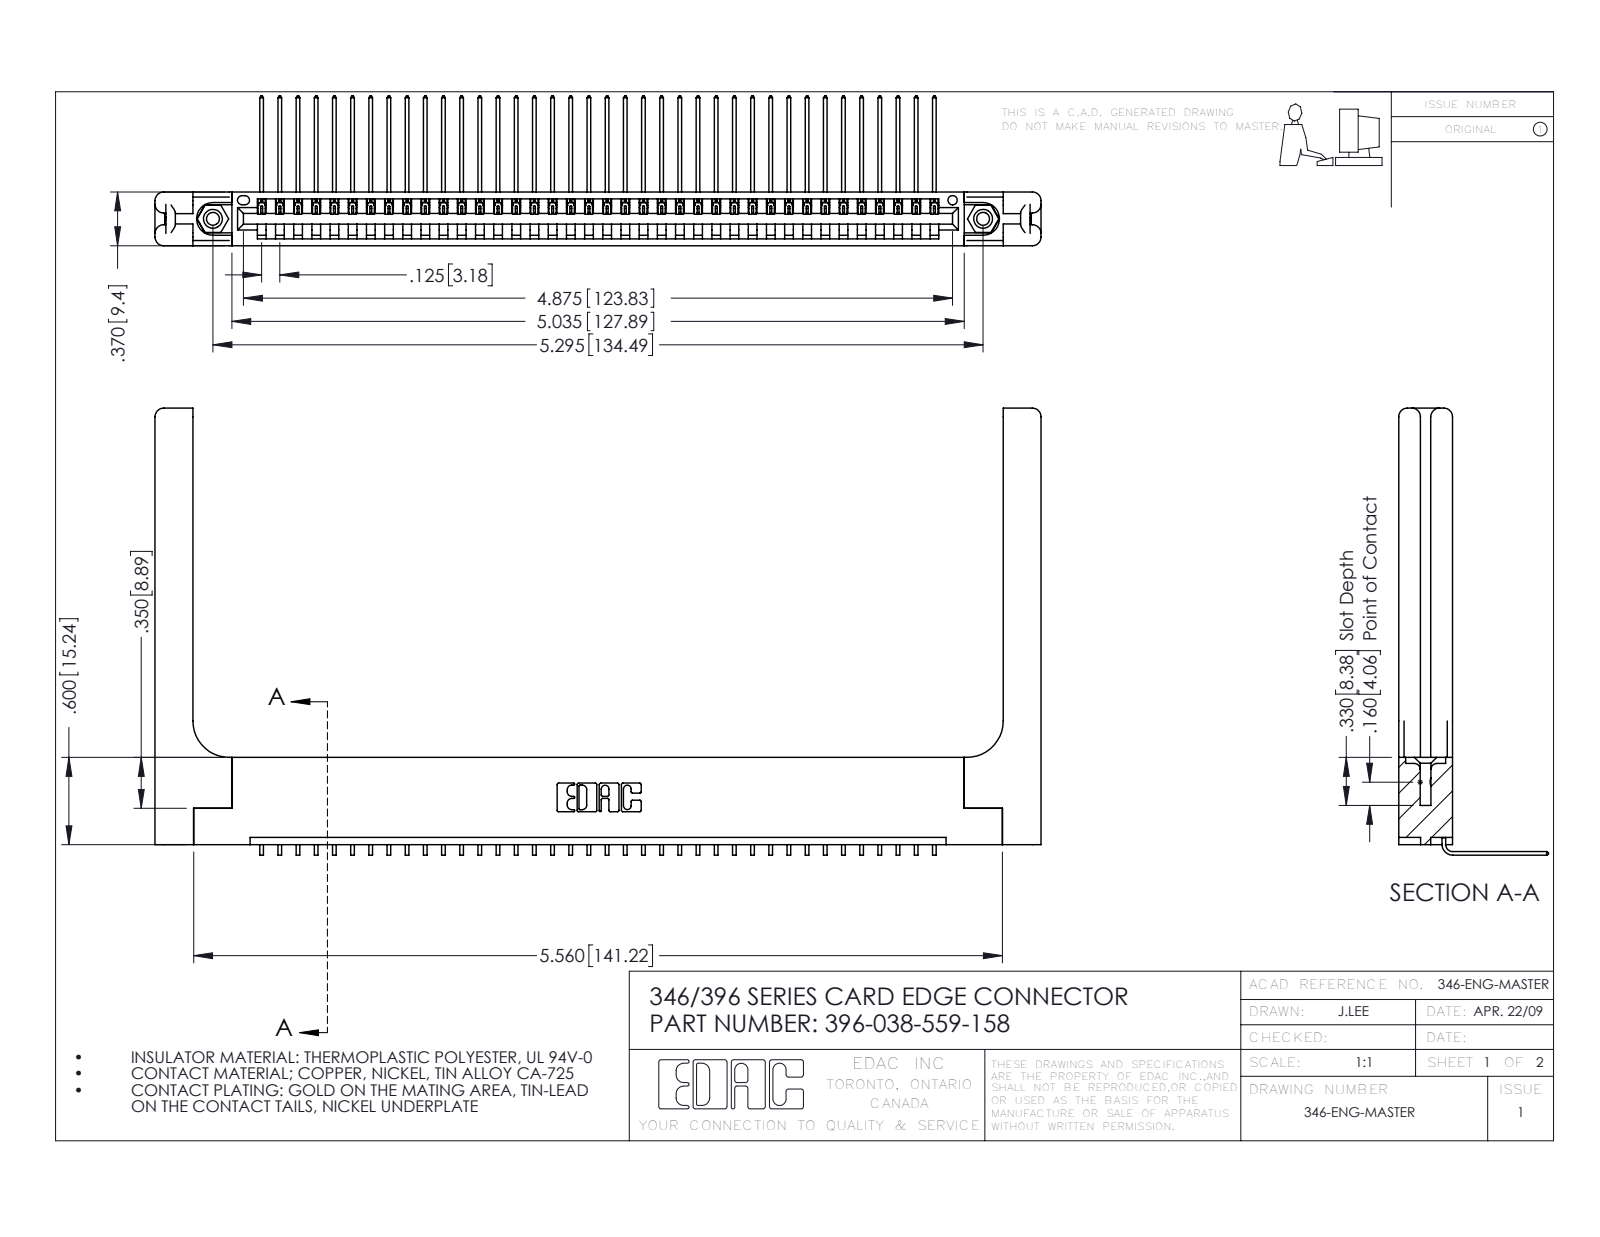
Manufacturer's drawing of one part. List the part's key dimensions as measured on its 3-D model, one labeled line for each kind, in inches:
Part name (STEP PRODUCT): 396-038-559-158; 345-292-001_558 559 Tail - 1; 346 Part_Flush Mounting Lugs - 0.156 Dia-TH; 346-220-058_345-220-058 (+1 more)
STEP written by: SolidWorks 2016 (CONFIG_CONTROL_DESIGN)
Units: inches
Bodies: 43 solids, 2658 faces (1820 planar, 778 cylindrical, 60 other)
Overall size (bounding box): 6.091 × 3.073 × 1.03
Volume: 1.369 in³ · Surface area: 38 in²
Round holes (diameter × count): ⌀0.089 ×2, ⌀0.125 ×2, ⌀0.156 ×2, ⌀0.064 ×1
Round bosses / shafts (diameter × count): ⌀0.155 ×2
Partial cylindrical surfaces — rounded edges, fillets, slot ends (radius × count): R0.006 ×76, R0.01 ×22, R0.06 ×16, R0.007 ×6, R0.031 ×6, R0.026 ×3, R0.03 ×2, R0.031 ×2
Main face-to-face distances: 0.37, 0.048, 0.072, 0.322, 0.148, 0.15, 0.025, 0.25, 0.298, 0.222
Hole centre spacings: 0.246, 5.086, 5.295
